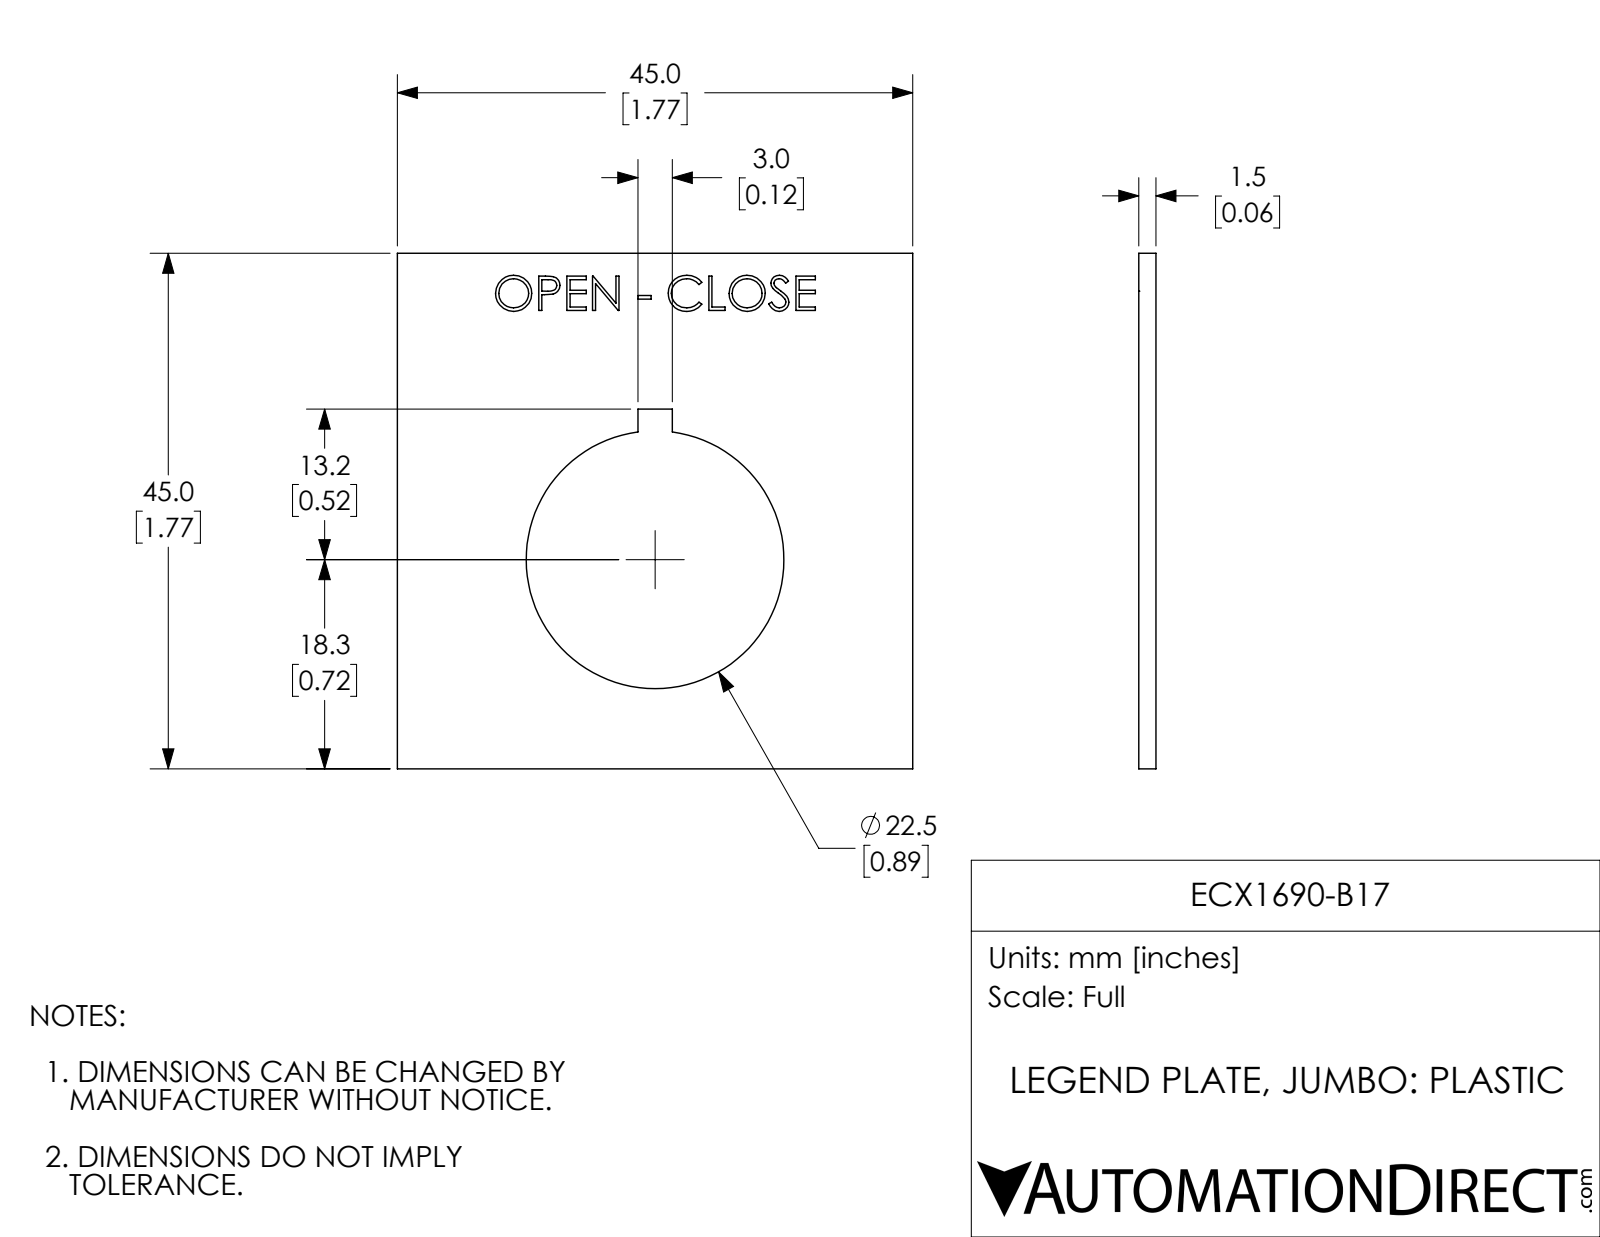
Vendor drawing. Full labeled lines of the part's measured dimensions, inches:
Part name (STEP PRODUCT): ECX1690-B17
STEP written by: SolidWorks 2018 (AUTOMOTIVE_DESIGN)
Units: inches
Bodies: 1 solid, 127 faces (78 planar, 3 cylindrical, 46 other)
Overall size (bounding box): 1.772 × 1.772 × 0.059
Volume: 0.148 in³ · Surface area: 5.624 in²
Round holes (diameter × count): ⌀0.886 ×1
Main face-to-face distances: 0.059, 1.772, 0.058, 0.827, 0.945, 1.236, 0.535, 0.118, 0.091, 0.244
